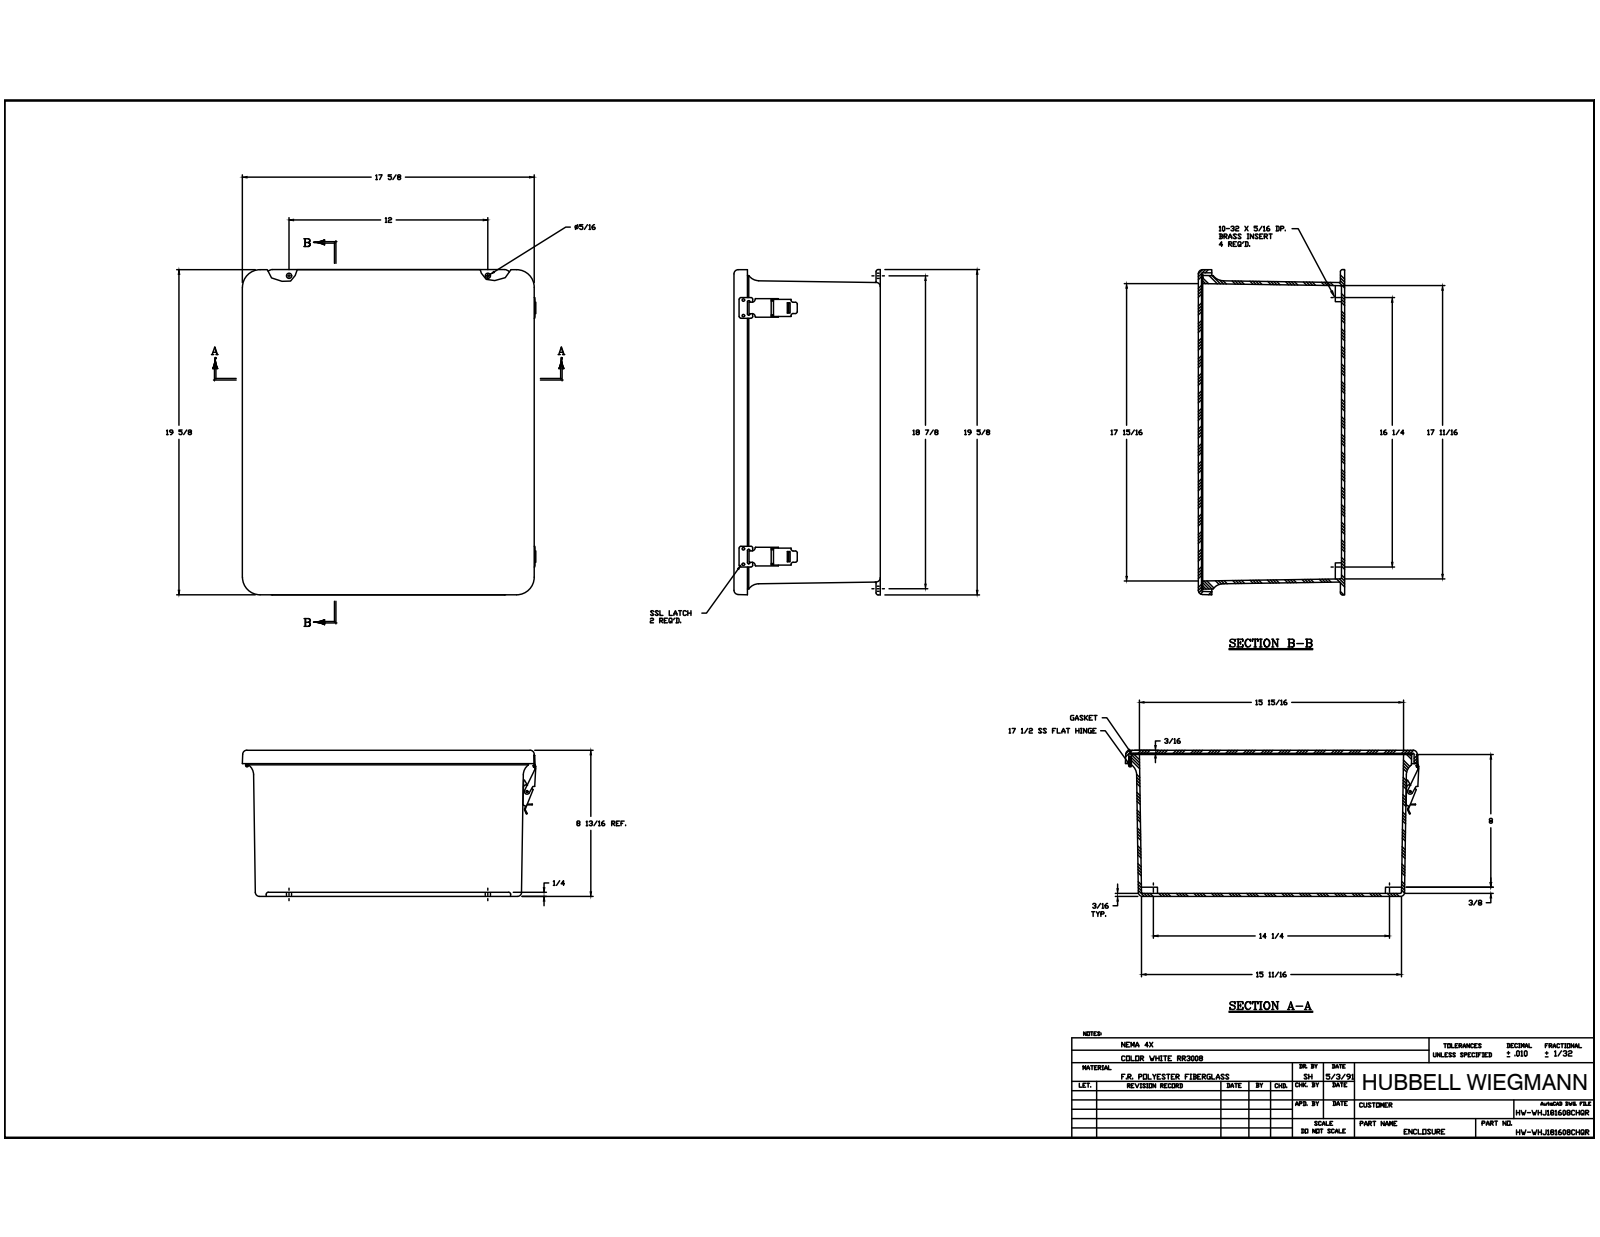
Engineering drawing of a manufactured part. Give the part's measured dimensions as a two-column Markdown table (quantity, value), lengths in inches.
| quantity | value |
| --- | --- |
| part name | J1816HL_2; RMINS45821P_79; RMINS45821P_80; RMINS45821P_81 (+8 more) |
| STEP written by | Autodesk Inventor 2014 (AUTOMOTIVE_DESIGN) |
| units | inches |
| bodies | 42 solids, 1133 faces (509 planar, 473 cylindrical, 151 other) |
| overall size | 19.625 × 17.706 × 8.826 |
| volume | 260.3 in³ |
| surface area | 2 731 in² |
| round holes (diameter × count) | 0.14 × 24, 0.131 × 12, 0.104 × 8, 0.152 × 5, 0.13 × 4, 0.156 × 4, 0.218 × 4, 0.135 × 2, 0.375 × 2, 0.085 × 1, 0.085 × 1 |
| round bosses / shafts (diameter × count) | 0.125 × 20, 0.25 × 12, 0.27 × 4, 0.3 × 1, 0.17 × 1, 0.155 × 1, 0.12 × 1 |
| partial cylindrical surfaces (radius × count) | 0.015 × 20, 0.031 × 20, 0.125 × 20, 0.045 × 16, 0.03 × 12, 0.022 × 9, 0.25 × 8, 0.06 × 6 |
| main face-to-face distances | 0.187, 8.638, 8.826, 0.188, 8.45, 8.638, 0.302, 0.49, 8.563, 8.375 |
| hole center spacings | 3.375, 3.375, 6.75, 0.25, 10.25, 14.984, 9.75, 10 |
